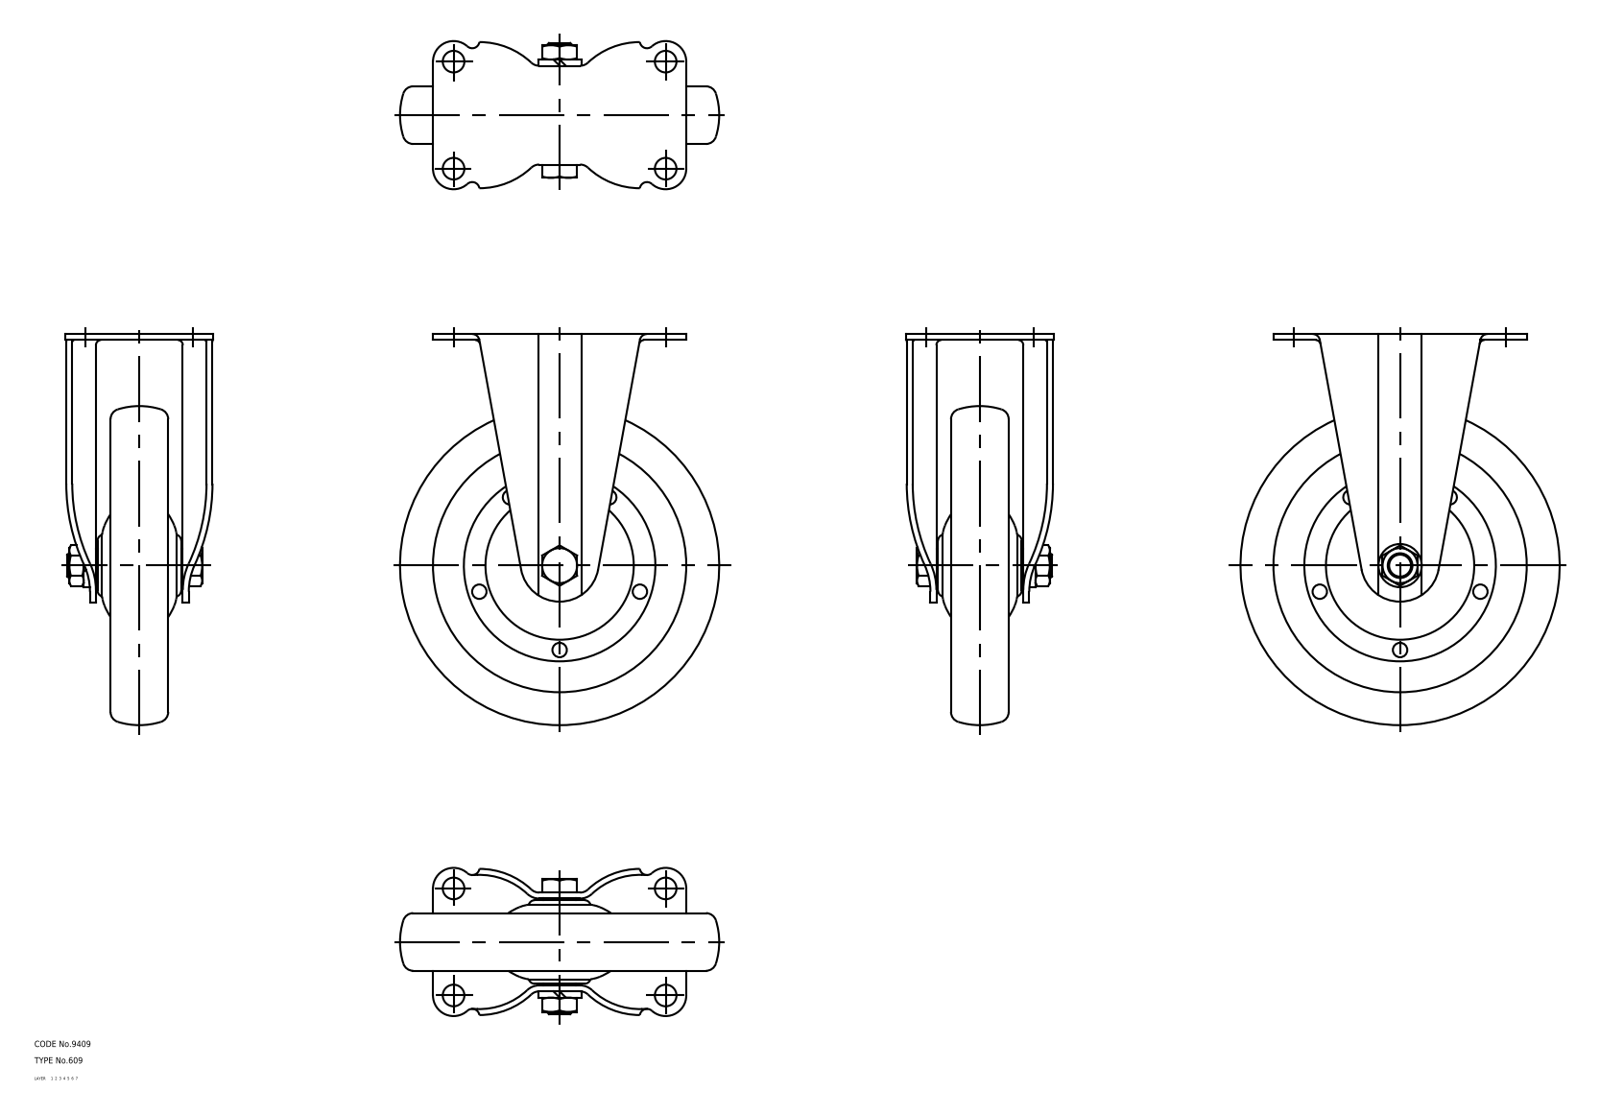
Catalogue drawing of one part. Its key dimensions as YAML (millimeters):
part_name: "67121053; 67121066; 67121079"
step_written_by: "CADfix (AUTOMOTIVE_DESIGN)"
units: millimeters
bodies: {solids: 3, faces: 184, planar: 0, cylindrical: 0, other: 184}
overall_size: [190, 155, 72]
volume: 516146
surface_area: 102699
